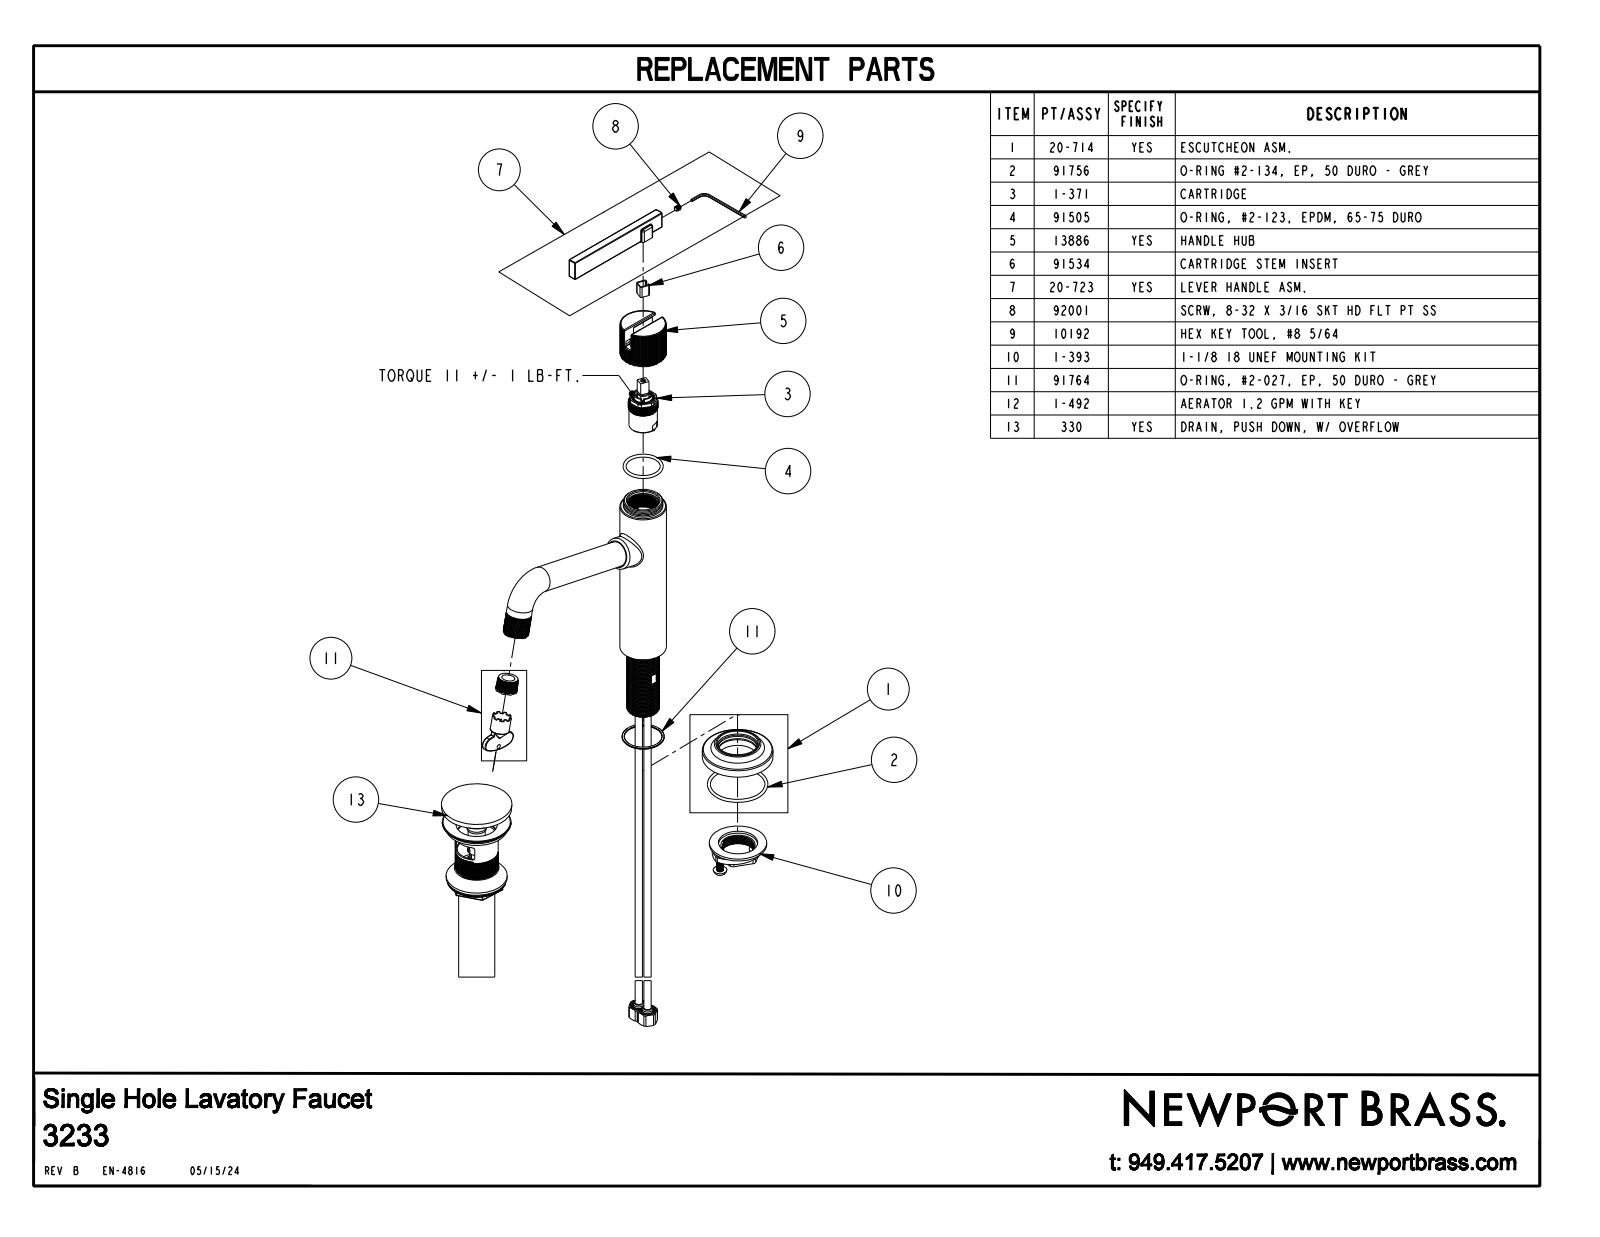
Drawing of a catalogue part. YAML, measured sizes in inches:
part_name: "3233_SW0001"
step_written_by: "CREO PARAMETRIC BY PTC INC, 2023134 (CONFIG_CONTROL_DESIGN)"
units: inches
bodies: {solids: 1, faces: 650, planar: 361, cylindrical: 237, other: 52}
overall_size: [7.825, 7.754, 2.43]
volume: 20.76
surface_area: 82.02
round_holes:
  - {diameter: 1.394, count: 1}
round_bosses_or_shafts:
  - {diameter: 0.875, count: 2}
  - {diameter: 2.43, count: 1}
  - {diameter: 1.6, count: 1}
  - {diameter: 1.51, count: 1}
  - {diameter: 1.1, count: 1}
partial_cylinders:
  - {radius: 0.02, count: 19}
  - {radius: 0.03, count: 12}
  - {radius: 0.06, count: 8}
  - {radius: 0.13, count: 6}
  - {radius: 0.04, count: 4}
  - {radius: 0.01, count: 2}
  - {radius: 0.353, count: 1}
  - {radius: 0.45, count: 1}
face_to_face_distances: [0.3, 7.754, 7.738, 0.016, 7.028, 0.709, 0.725, 7.038, 0.7, 0.716]
